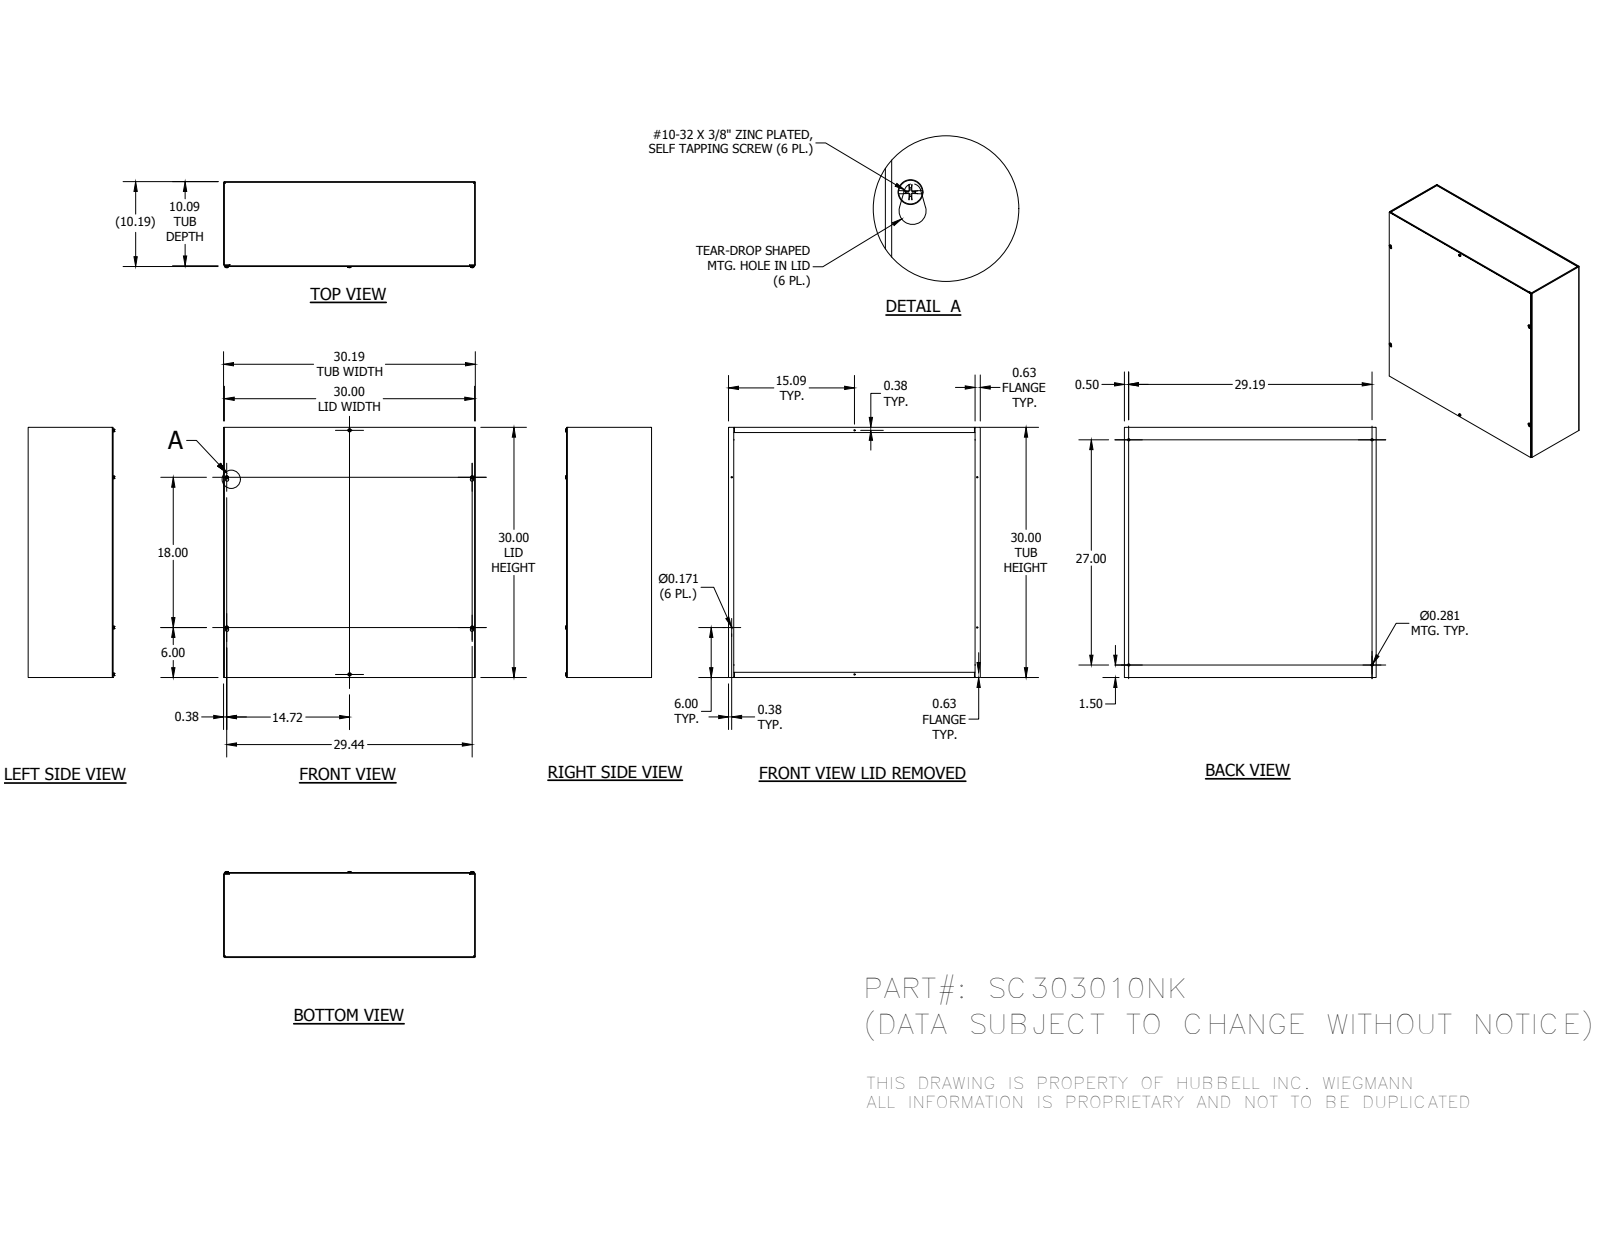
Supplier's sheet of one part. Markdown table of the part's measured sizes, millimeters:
| quantity | value |
| --- | --- |
| part name | SC303010NKBLR; SC3010NKTB; SC3030LPA; 37214 (+1 more) |
| STEP written by | Autodesk Inventor 2014 (AUTOMOTIVE_DESIGN) |
| units | millimeters |
| bodies | 10 solids, 404 faces (232 planar, 50 cylindrical, 122 other) |
| overall size | 766.76 × 762 × 262.11 |
| volume | 4 782 000 mm³ |
| surface area | 4 045 000 mm² |
| round holes (diameter × count) | 4.34 × 6, 7.14 × 4, 7.92 × 2 |
| round bosses / shafts (diameter × count) | 4.83 × 6 |
| partial cylindrical surfaces (radius × count) | 0.4 × 12, 2.78 × 12, 3.17 × 4, 5.16 × 4 |
| main face-to-face distances | 2.38, 256.38, 254, 258.76, 762, 759.62, 764.38, 757.24, 766.76, 4.76 |
| hole center spacings | 114.34, 371.78, 400.23, 571.51, 707, 753.26, 804.82, 938.59 |
